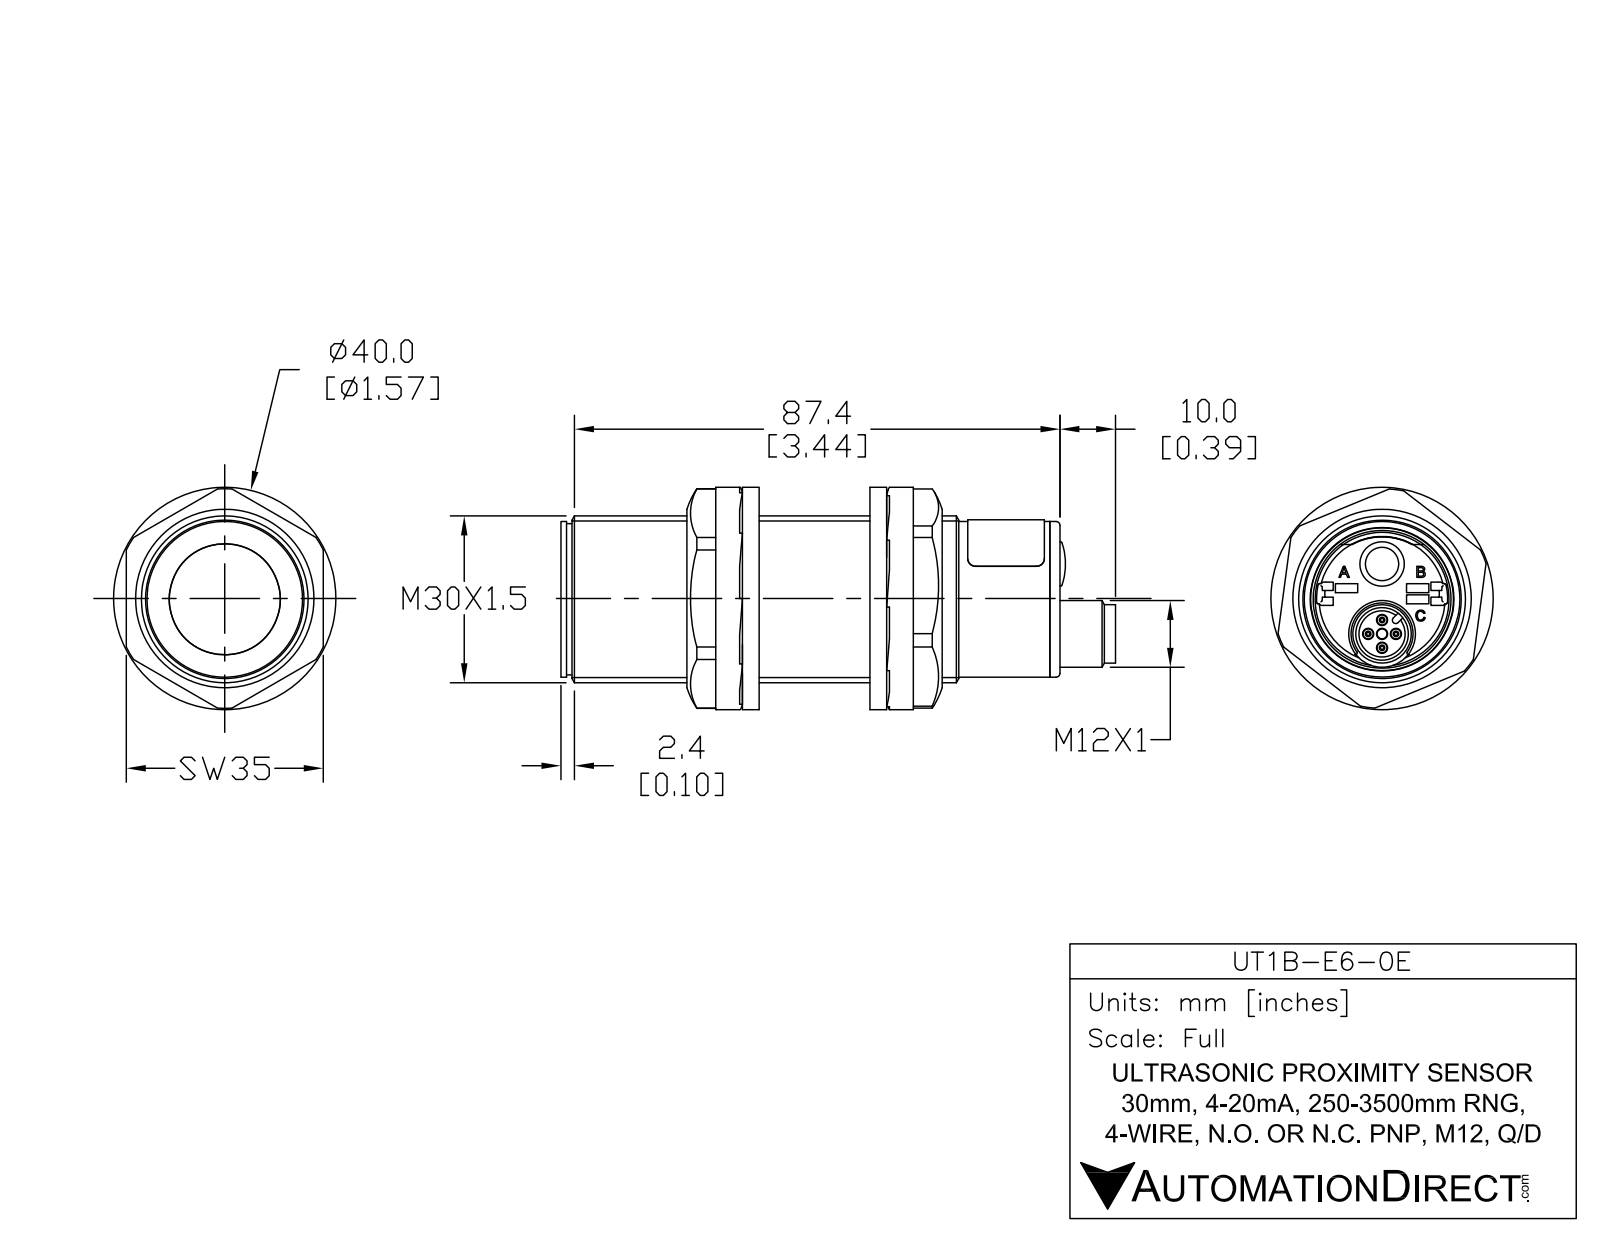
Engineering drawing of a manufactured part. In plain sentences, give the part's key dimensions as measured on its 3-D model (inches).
The part is named "UT1B-E6-0E". Its 3-D file was written by "SolidWorks 2017 (AUTOMOTIVE_DESIGN)". It is 5 solids with 107 faces: 30 planar, 45 cylindrical and 32 other. Overall it measures 3.89 by 1.181 by 1.181 inches. Its volume is 3.754 cubic inches and its surface area 20.71 square inches. Round holes: 4 of diameter 0.071, 1 of diameter 0.315, 1 of diameter 0.327, 1 of diameter 0.372, 1 of diameter 0.925. Round bosses or shafts: 4 of diameter 0.039, 1 of diameter 1.181, 1 of diameter 1.102, 1 of diameter 1.071, 1 of diameter 0.472, 1 of diameter 0.413, 1 of diameter 0.364. Partial cylindrical surfaces (rounded edges, fillets, slot ends): 2 of radius 0.012, 1 of radius 0.024. The main face-to-face distances are 3.386, 3.457, 0.039, 3.425, 0.071, 3.496, 0.039, 0.059, 3.425, 3.496. The hole center spacings are 0.098, 0.139, 0.197, 0.264, 0.505, 0.146, 0.245, 0.25.
